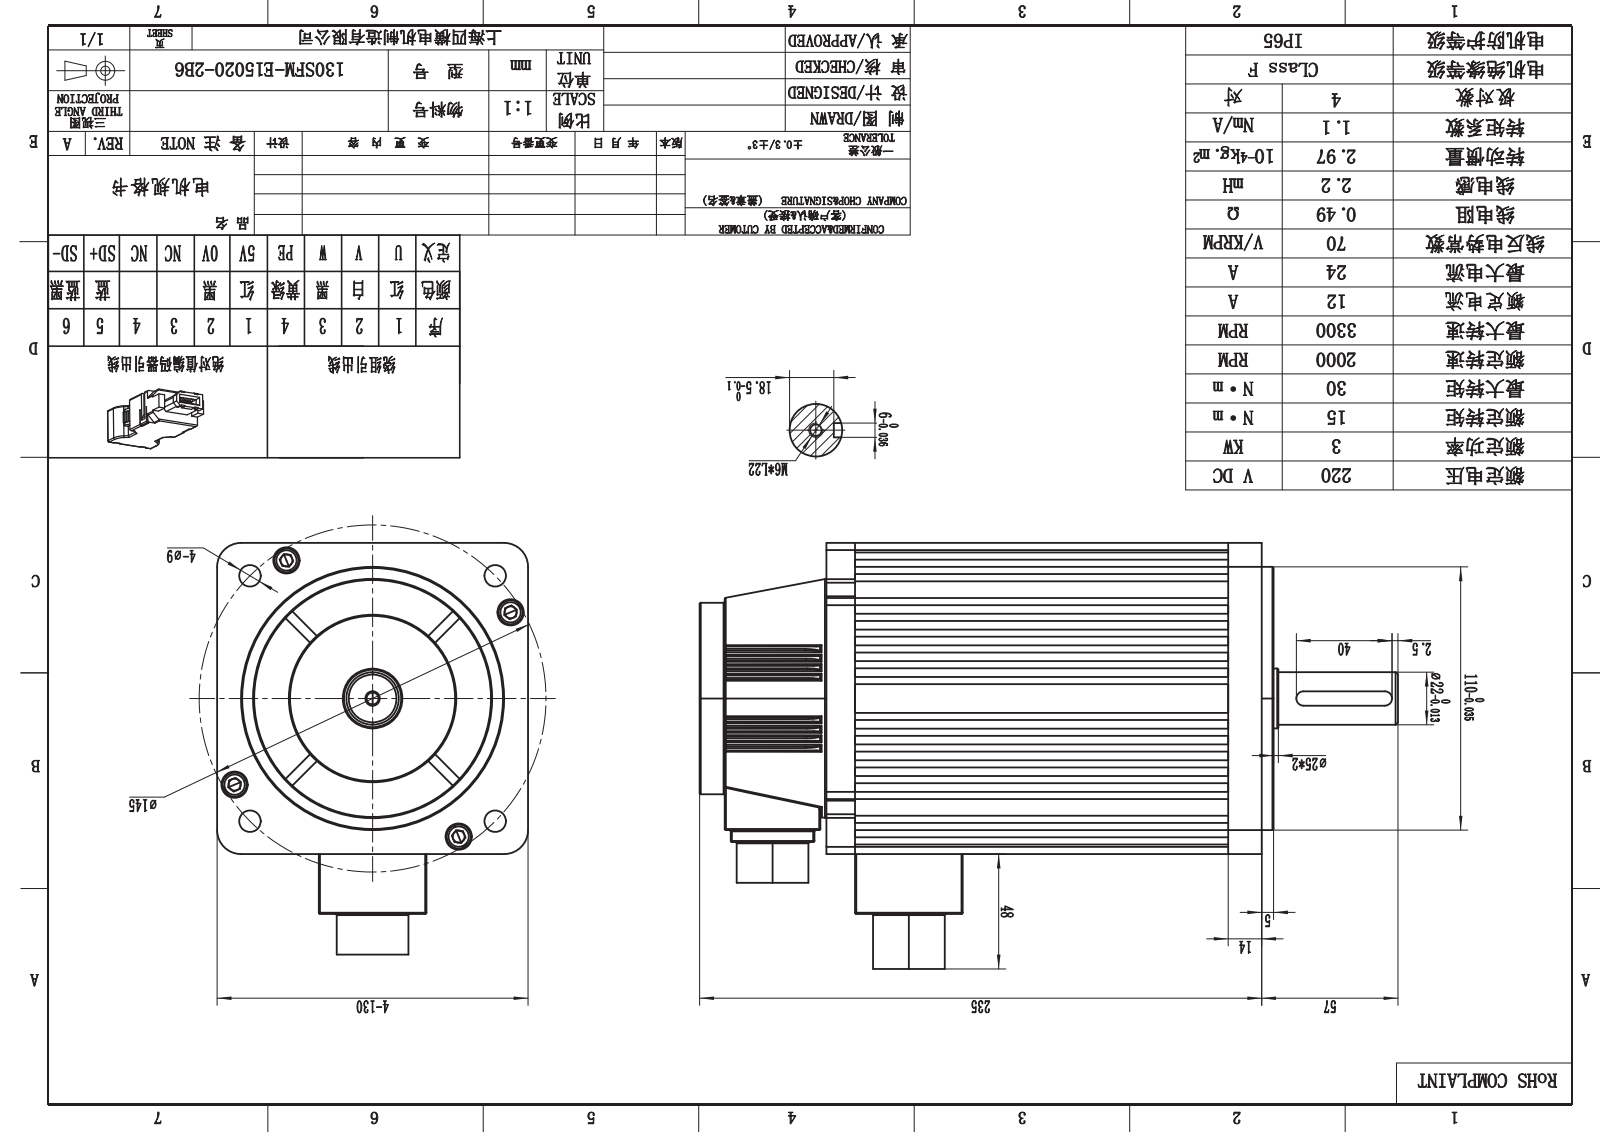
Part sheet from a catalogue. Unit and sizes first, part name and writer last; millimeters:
Units: millimetres
Overall size (bounding box): 290 × 262.4 × 130
Round holes (diameter × count): ⌀1 ×15, ⌀2.5 ×6, ⌀3.4 ×4, ⌀6 ×4, ⌀6.5 ×4, ⌀9 ×4, ⌀11 ×4, ⌀2.9 ×2, ⌀3.5 ×2, ⌀3.8 ×2, ⌀5 ×1, ⌀7 ×1
Round bosses / shafts (diameter × count): ⌀1.5 ×15, ⌀0.6 ×15, ⌀1 ×12, ⌀6 ×8, ⌀10 ×4, ⌀3.5 ×3, ⌀4.5 ×2, ⌀3.3 ×2
Partial cylindrical surfaces — rounded edges, fillets, slot ends (radius × count): R0.5 ×108, R1 ×53, R0.45 ×48, R0.2 ×24, R2 ×22, R0.97 ×15, R3 ×10, R1.5 ×8
Main face-to-face distances: 153.5, 12, 165.5, 130, 2, 128, 14, 21, 179.5, 167.5
Hole centre spacings: 2.24, 3.63, 4.03, 2.02, 3.62, 4.48, 5.42, 5.68
Volume: 3 102 000 mm³ · Surface area: 296 953 mm²
Bodies: 42 solids, 2140 faces (817 planar, 737 cylindrical, 586 other)
Part name (STEP PRODUCT): 02-0.step.STEP.STEP.STEP; 130________.step.STEP.STEP.STEP; 02.A037.000134 M130AIS133-C15020-B1-4-1R; hexagon socket head cap screws gb_GB_FASTENER_SCREWS_HSHCS M6X20-N.step.STEP.STEP.STEP (+5 more)
STEP written by: SolidWorks 2020 (AUTOMOTIVE_DESIGN)
